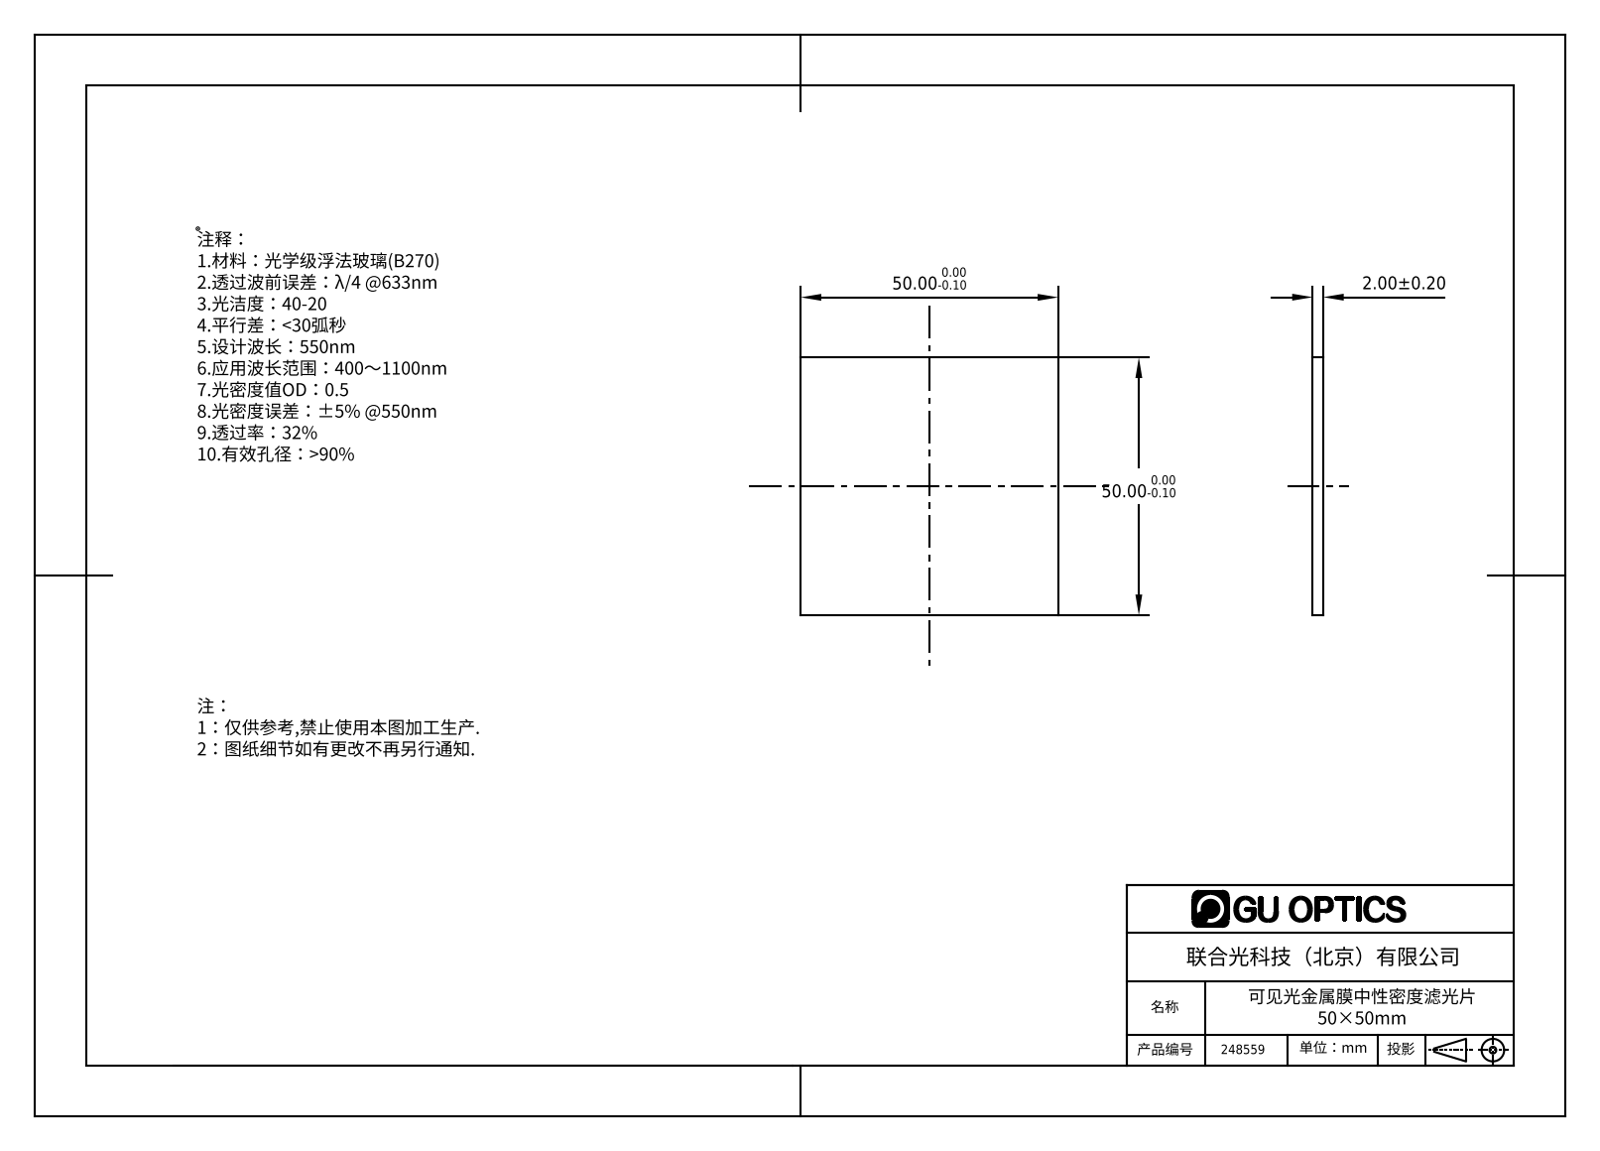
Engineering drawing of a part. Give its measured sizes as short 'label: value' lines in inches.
name: 248555
written by: SolidWorks 2016 (AUTOMOTIVE_DESIGN)
unit: in
bodies: 1 solid, 6 faces (6 planar, 0 cylindrical, 0 other)
size: 1.969 × 1.969 × 0.079
volume: 0.305 in³; area: 8.37 in²
face distances: 0.079, 1.969
